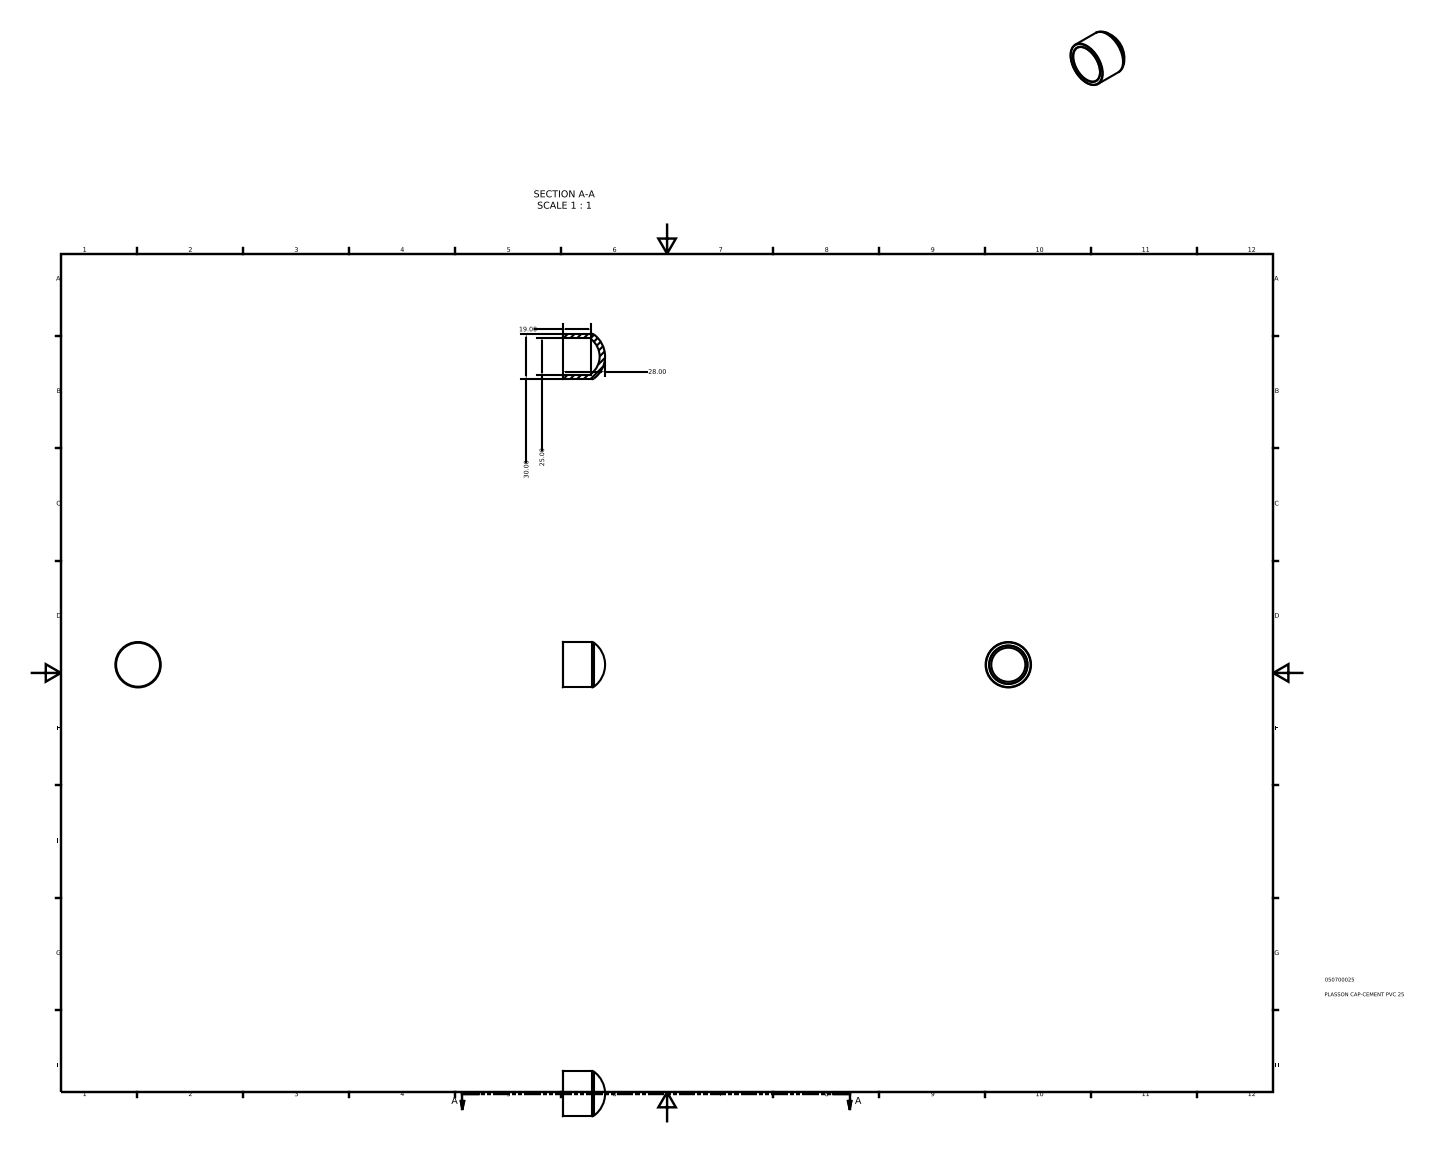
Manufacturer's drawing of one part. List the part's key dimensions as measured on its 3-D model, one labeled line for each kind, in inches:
Part name (STEP PRODUCT): 050700025
STEP written by: Autodesk Inventor 2015 (AUTOMOTIVE_DESIGN)
Units: inches
Bodies: 1 solid, 9 faces (2 planar, 2 cylindrical, 5 other)
Overall size (bounding box): 1.181 × 1.181 × 1.102
Volume: 0.411 in³ · Surface area: 7.84 in²
Round holes (diameter × count): ⌀0.984 ×1
Round bosses / shafts (diameter × count): ⌀1.181 ×1
Main face-to-face distances: 0.748
